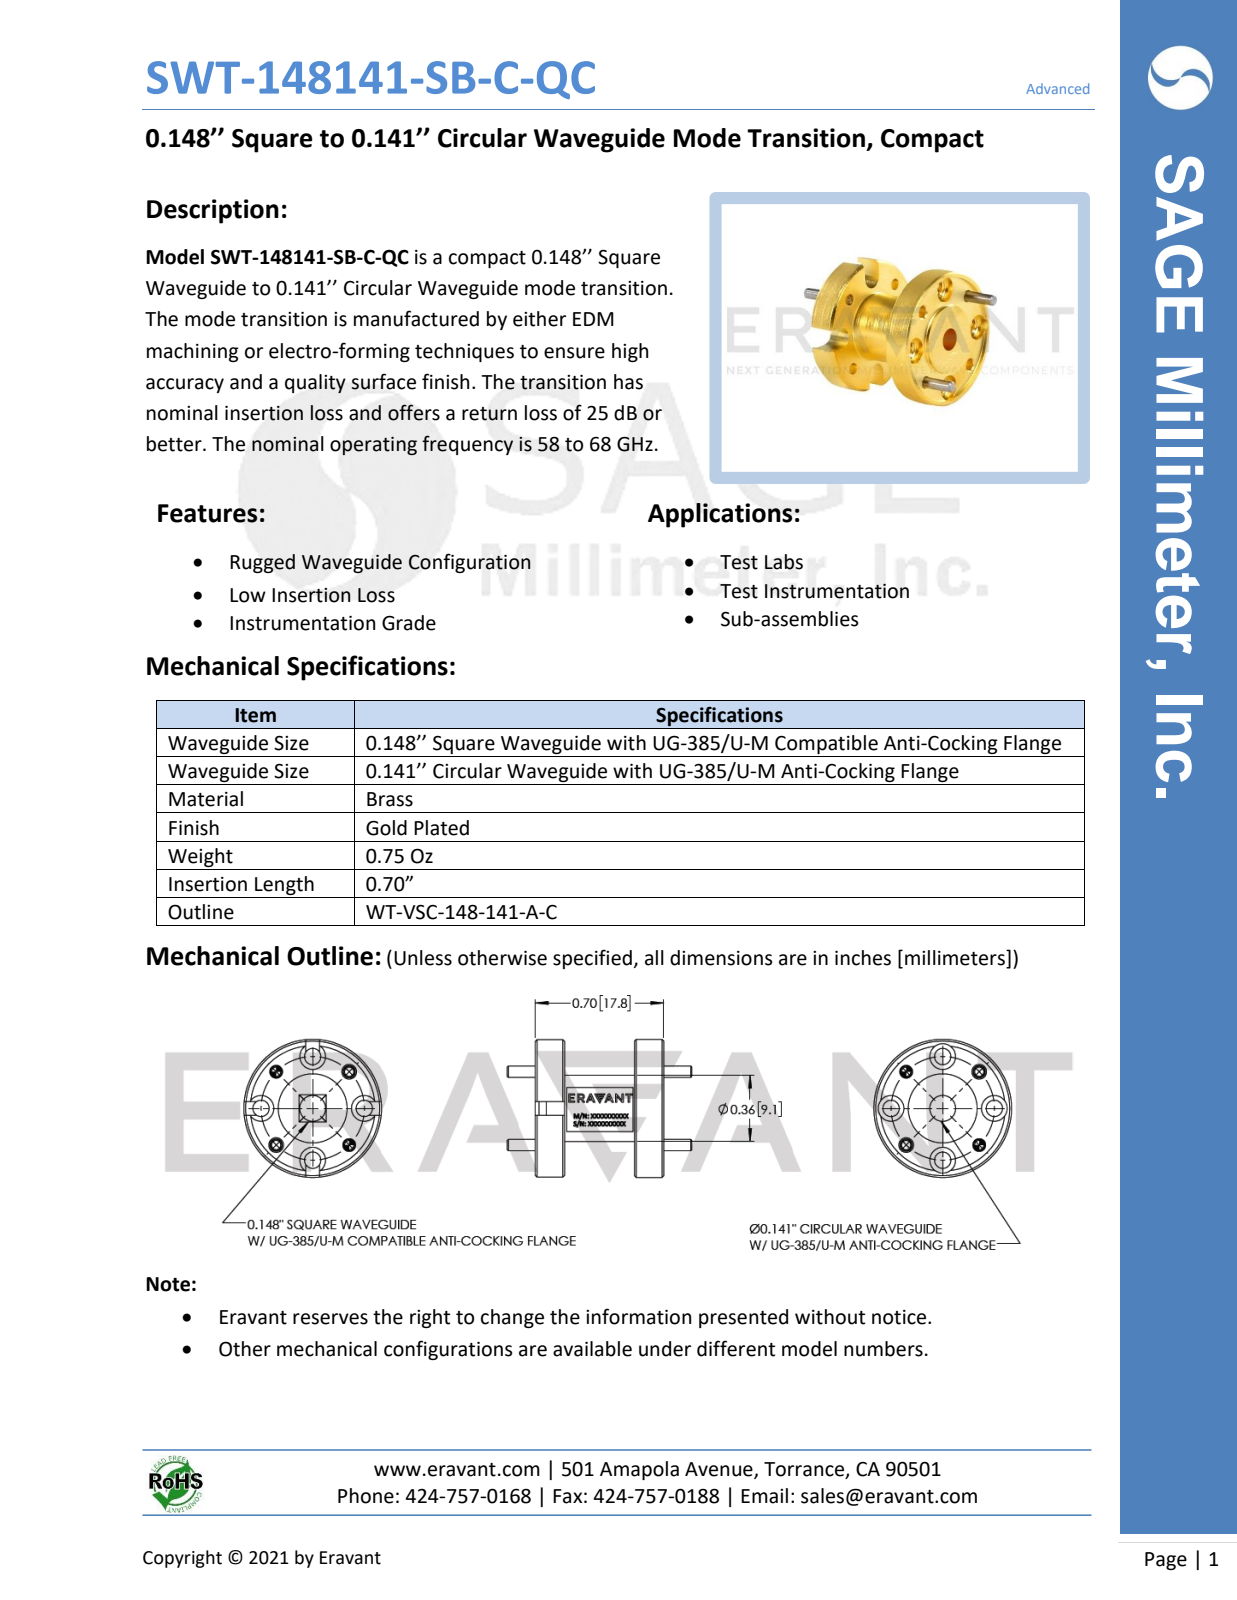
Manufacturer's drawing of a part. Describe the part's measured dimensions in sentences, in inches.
The part is named "WT-VSC-148-141-A-C, Defeatured". Its 3-D file was written by "SolidWorks 2021 (AUTOMOTIVE_DESIGN)". It is 5 solids with 176 faces: 46 planar, 78 cylindrical and 52 other. Overall it measures 1.005 by 0.75 by 0.75 inches. Its volume is 0.157 cubic inches and its surface area 3.449 square inches. Round holes: 4 of diameter 0.061, 4 of diameter 0.067, 4 of diameter 0.089, 4 of diameter 0.14, 1 of diameter 0.68. Round bosses or shafts: 4 of diameter 0.063, 1 of diameter 0.75, 1 of diameter 0.375, 1 of diameter 0.36. The main face-to-face distances are 0.14, 0.52, 0.02, 0.16, 0.54, 0.68, 0.38, 0.66, 0.7, 0.06. The hole center spacings are 0.215, 0.281, 0.398, 0.519, 0.562.
